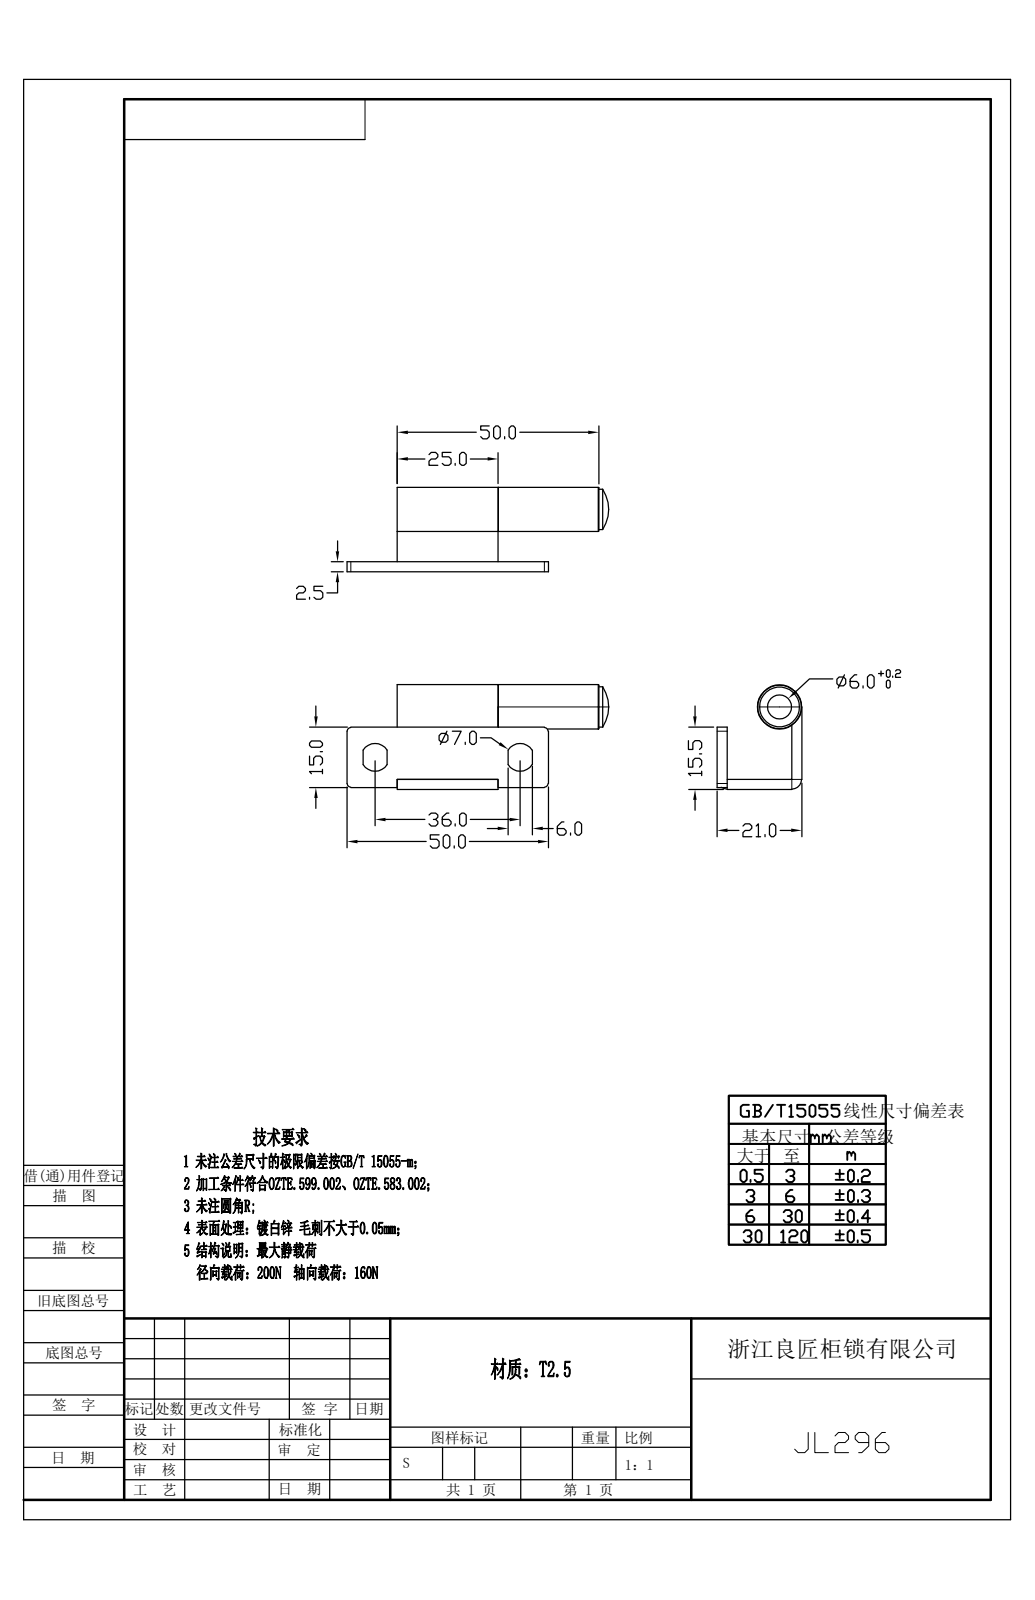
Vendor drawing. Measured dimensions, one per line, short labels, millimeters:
written by: Rhino 8.5 (CONFIG_CONTROL_DESIGN)
unit: mm
bodies: 2 solids, 56 faces (30 planar, 20 cylindrical, 6 other)
size: 65 × 26 × 21
volume: 6 845 mm³; area: 7 521 mm²
holes: 1× ⌀6
bosses: 1× ⌀11, 1× ⌀10, 1× ⌀5.9
rounds: 4× R1, 2× R2.5, 2× R3.5
face distances: 2.5, 18.5, 21, 16, 25, 50, 15.5, 13, 12.5, 37.5
